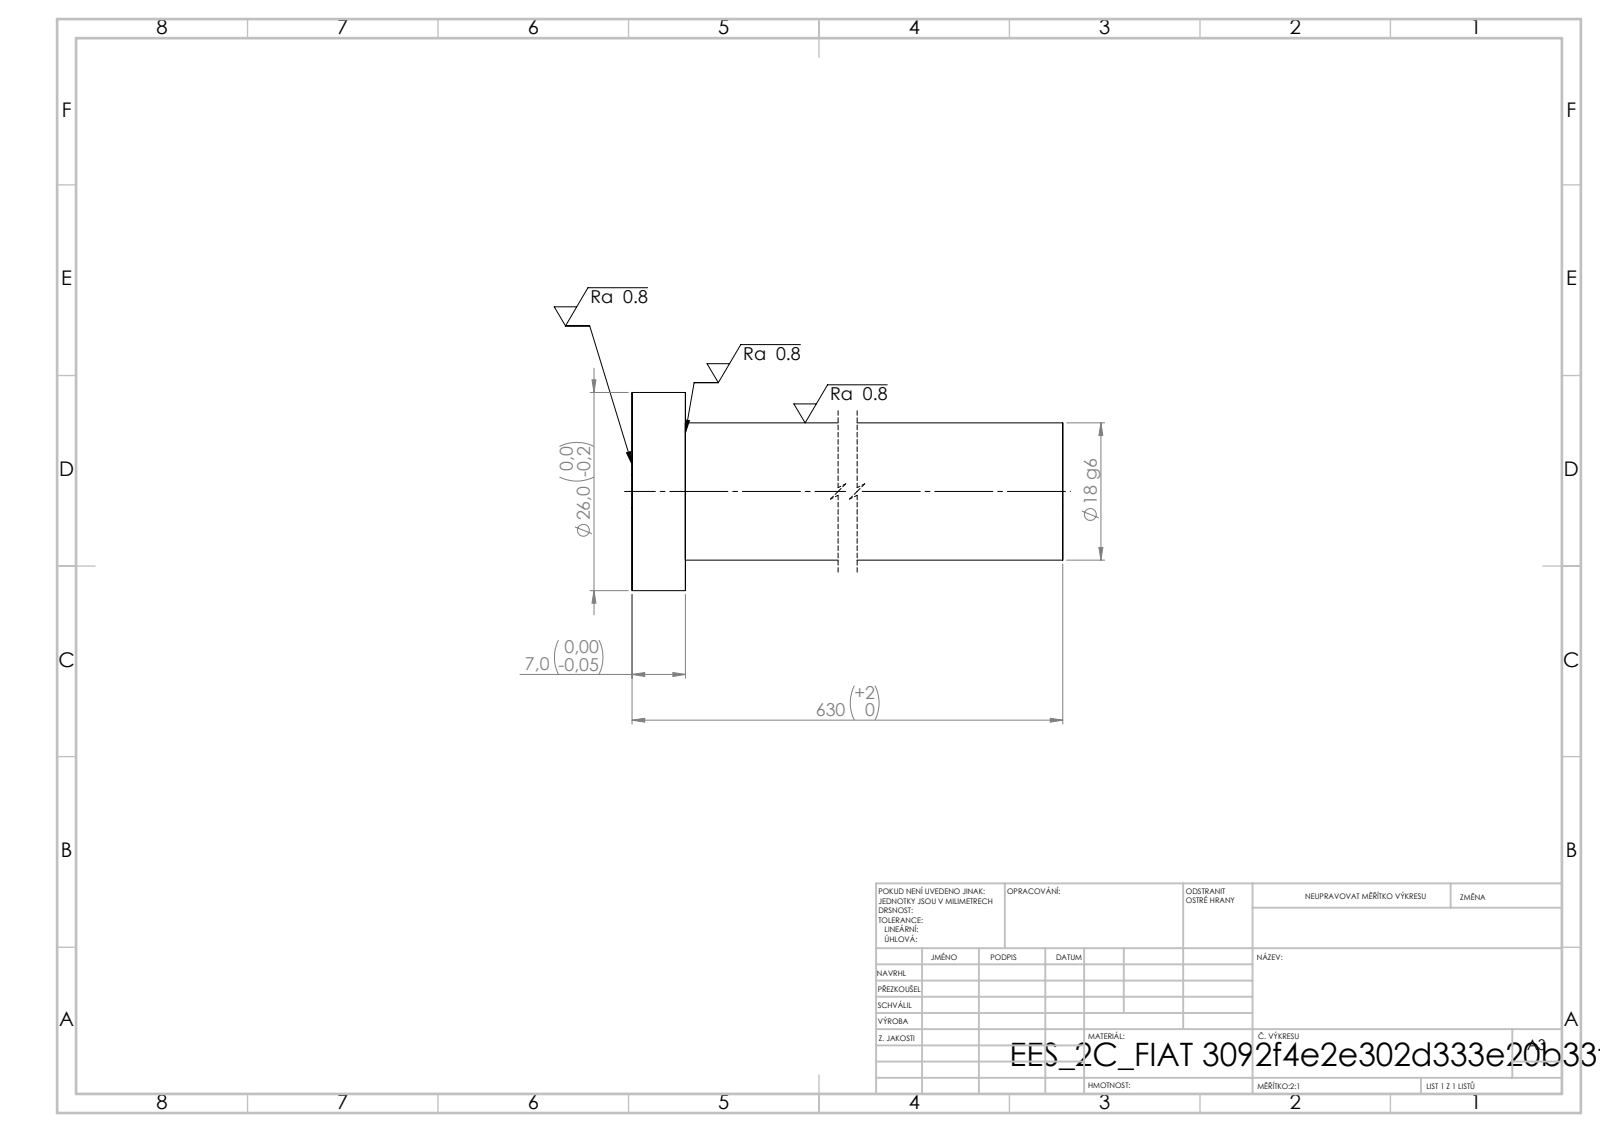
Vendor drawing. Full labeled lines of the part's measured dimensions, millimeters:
STEP written by: SolidWorks 2019 (CONFIG_CONTROL_DESIGN)
Units: millimetres
Bodies: 1 solid, 7 faces (3 planar, 4 cylindrical, 0 other)
Overall size (bounding box): 630 × 26 × 26
Volume: 162 251 mm³ · Surface area: 36 863 mm²
Round bosses / shafts (diameter × count): ⌀26 ×1, ⌀18 ×1
Main face-to-face distances: 7, 630, 623
